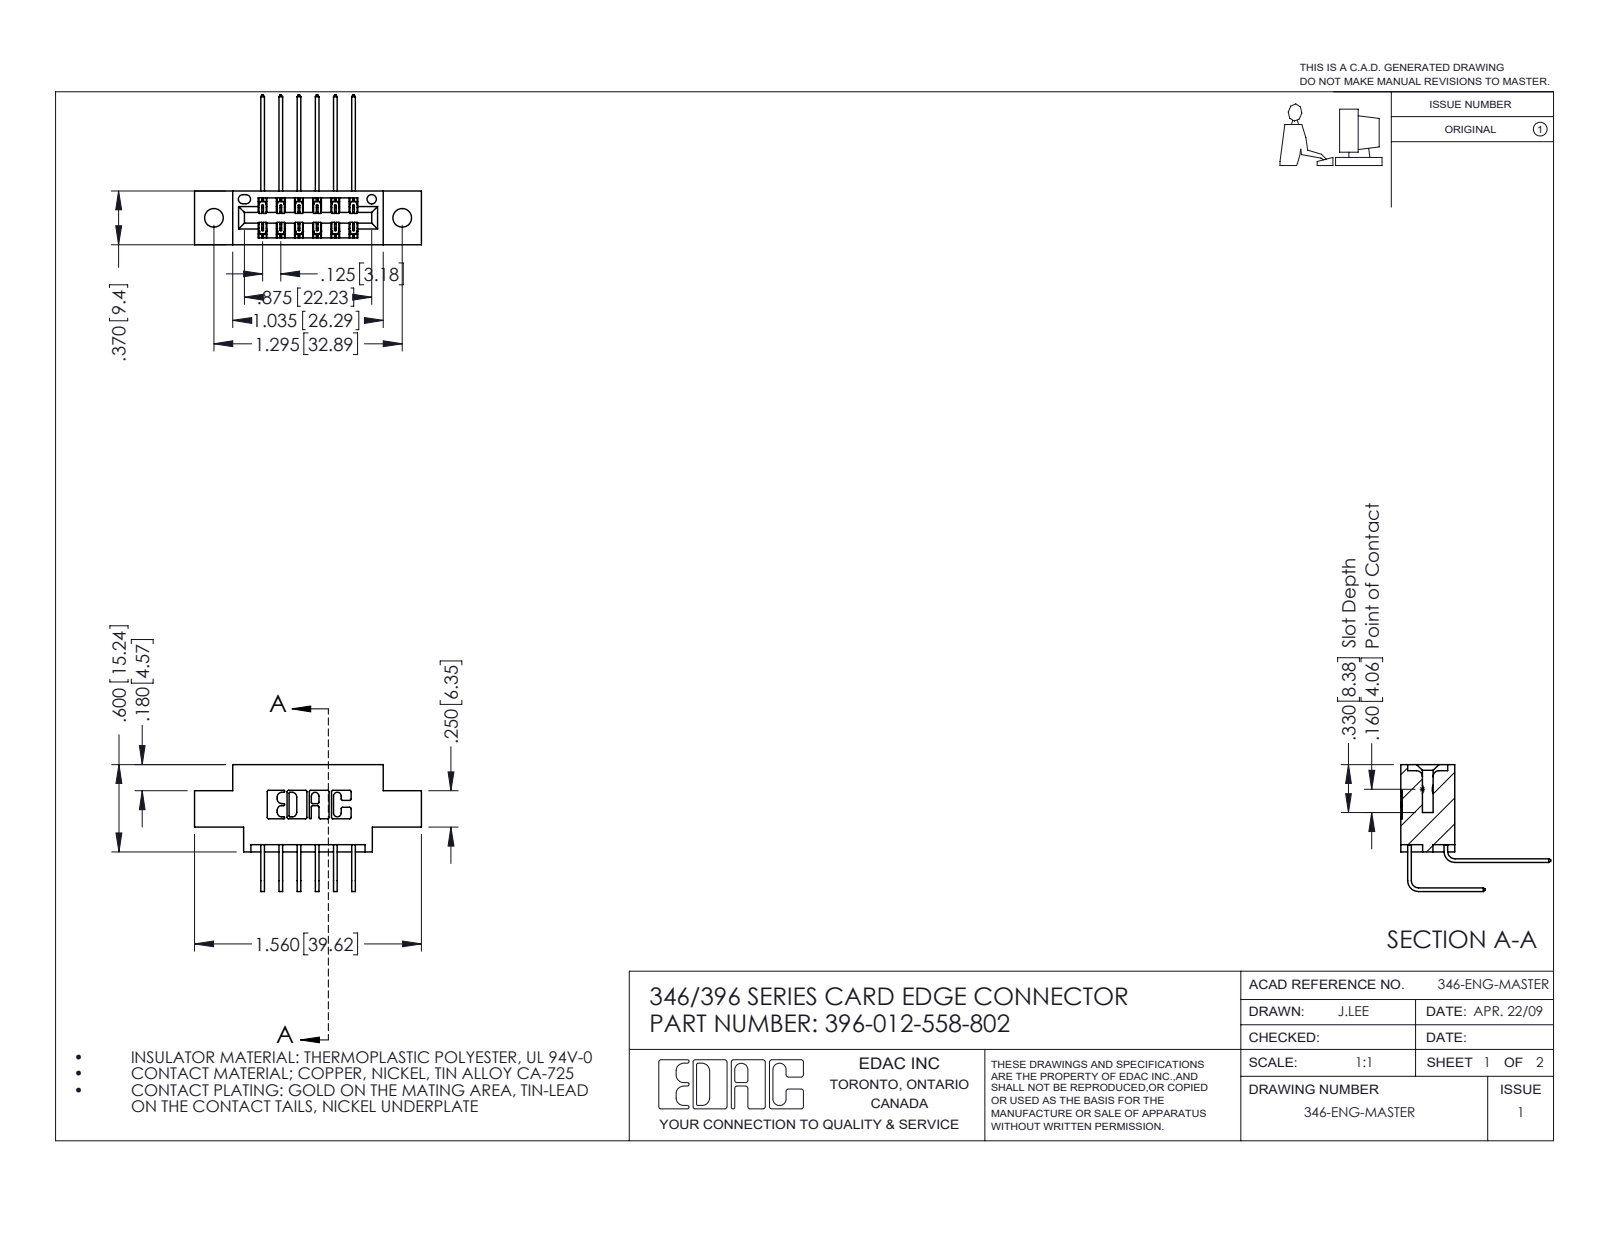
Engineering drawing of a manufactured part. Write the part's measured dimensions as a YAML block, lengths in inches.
part_name: "345-292-001_558 Tail - 2; 396-012-558-802; 346 Part_0.170 Offset - 0.128 Dia; 345-292-001_558 559 Tail - 1"
step_written_by: "SolidWorks 2016 (CONFIG_CONTROL_DESIGN)"
units: inches
bodies: {solids: 13, faces: 774, planar: 524, cylindrical: 250, other: 0}
overall_size: [1.56, 1.03, 0.873]
volume: 0.211
surface_area: 6.875
round_holes:
  - {diameter: 0.128, count: 2}
  - {diameter: 0.064, count: 1}
partial_cylinders:
  - {radius: 0.01, count: 22}
  - {radius: 0.006, count: 18}
  - {radius: 0.007, count: 6}
  - {radius: 0.031, count: 6}
  - {radius: 0.026, count: 3}
  - {radius: 0.014, count: 2}
  - {radius: 0.022, count: 2}
  - {radius: 0.024, count: 2}
face_to_face_distances: [0.25, 0.37, 0.048, 0.322, 0.025, 0.072, 0.298, 0.148, 0.222, 0.1]
hole_center_spacings: [0.246, 1.092, 1.295]
